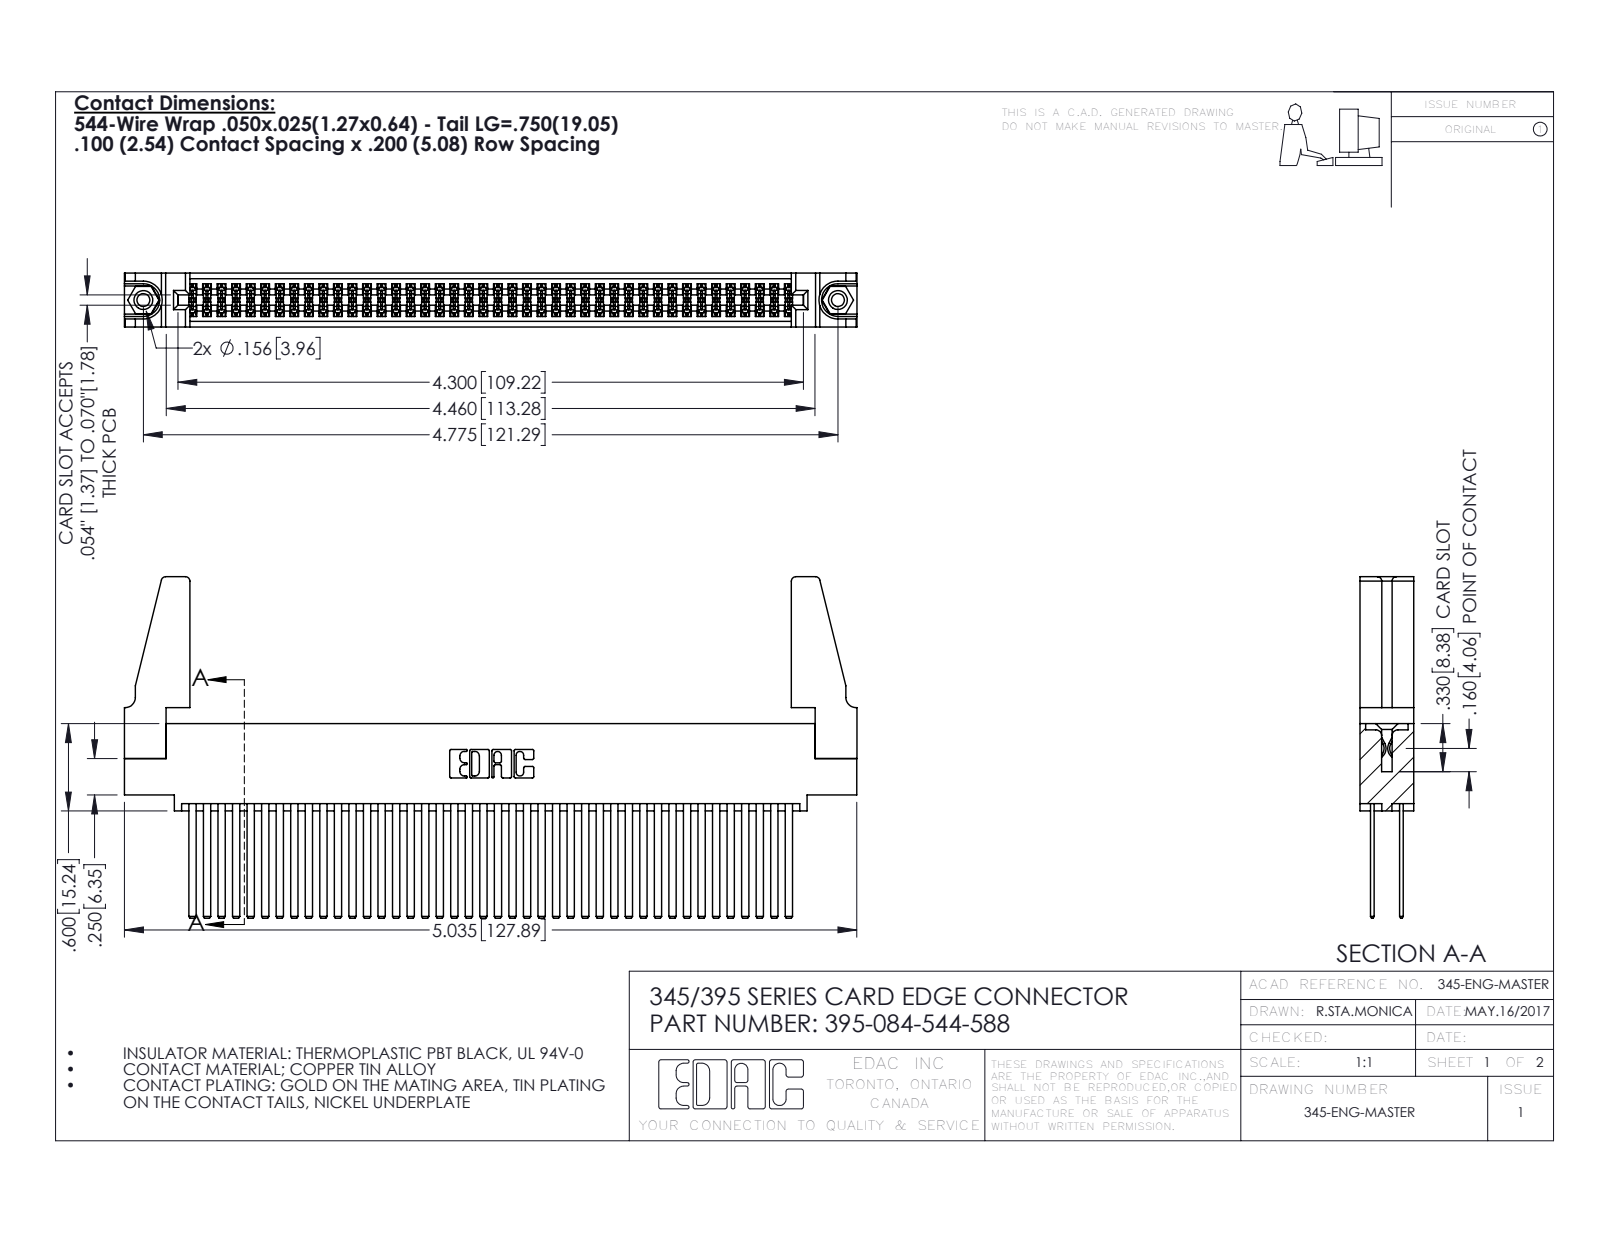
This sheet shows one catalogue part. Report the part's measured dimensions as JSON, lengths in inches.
{"part_name": "345 Part_0.110 Offset - 0.156 Dia-TH; 345-220-078_345-220-088; 345-250-001_345-250-001-102; 345-292-001_345-293-144 (+1 more)", "step_written_by": "SolidWorks 2016 (CONFIG_CONTROL_DESIGN)", "units": "inches", "bodies": {"solids": 89, "faces": 3950, "planar": 2592, "cylindrical": 1342, "other": 16}, "overall_size": [5.036, 2.347, 0.37], "volume_in3": 1.024, "surface_area_in2": 41.33, "round_holes": [[0.089, 2], [0.125, 2], [0.156, 2], [0.064, 1]], "round_bosses_or_shafts": [[0.155, 2]], "partial_cylinders_radius": [[0.006, 126], [0.01, 22], [0.03, 8], [0.007, 6], [0.031, 6], [0.026, 3], [0.014, 2], [0.019, 2]], "face_to_face_distances": [0.072, 0.298, 0.2, 0.098, 0.272, 0.025, 0.225, 0.37, 0.175, 0.149], "hole_center_spacings": [0.27, 4.539, 4.775]}
